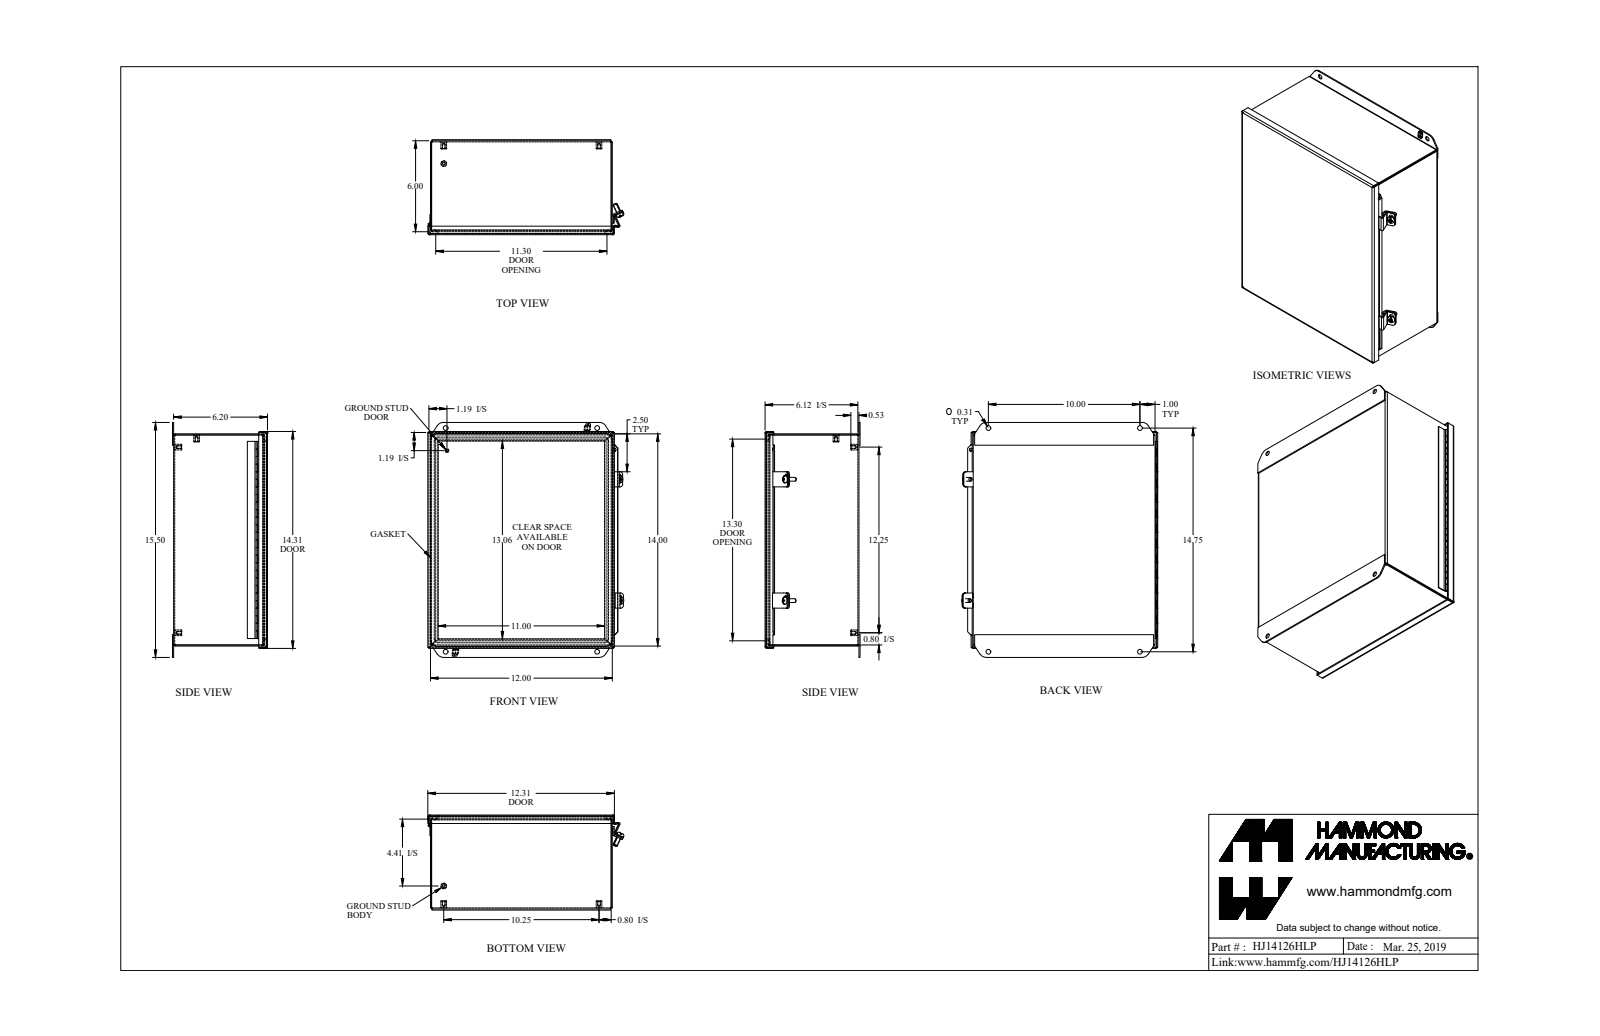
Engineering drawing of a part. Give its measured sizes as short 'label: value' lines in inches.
name: HJ14126HLP
written by: SolidWorks 2018 (AUTOMOTIVE_DESIGN)
unit: in
bodies: 20 solids, 809 faces (430 planar, 251 cylindrical, 128 other)
size: 15.5 × 12.937 × 6.269
volume: 58.18 in³; area: 1 632 in²
holes: 5× ⌀0.156, 4× ⌀0.313, 2× ⌀0.213, 1× ⌀0.05
bosses: 5× ⌀0.375, 3× ⌀0.25, 2× ⌀0.48, 1× ⌀0.188, 1× ⌀0.1, 1× ⌀0.045
rounds: 16× R0.25, 13× R0.036, 13× R0.108, 4× R0.01, 4× R0.029, 4× R0.086, 4× R0.141, 4× R0.188
face distances: 0.072, 6.125, 6.197, 6.053, 11.928, 13.928, 11.856, 12, 14, 13.856
hole spacings: 10.202, 1.256, 1.257, 10, 10.25, 12.25, 13.5, 13.5
